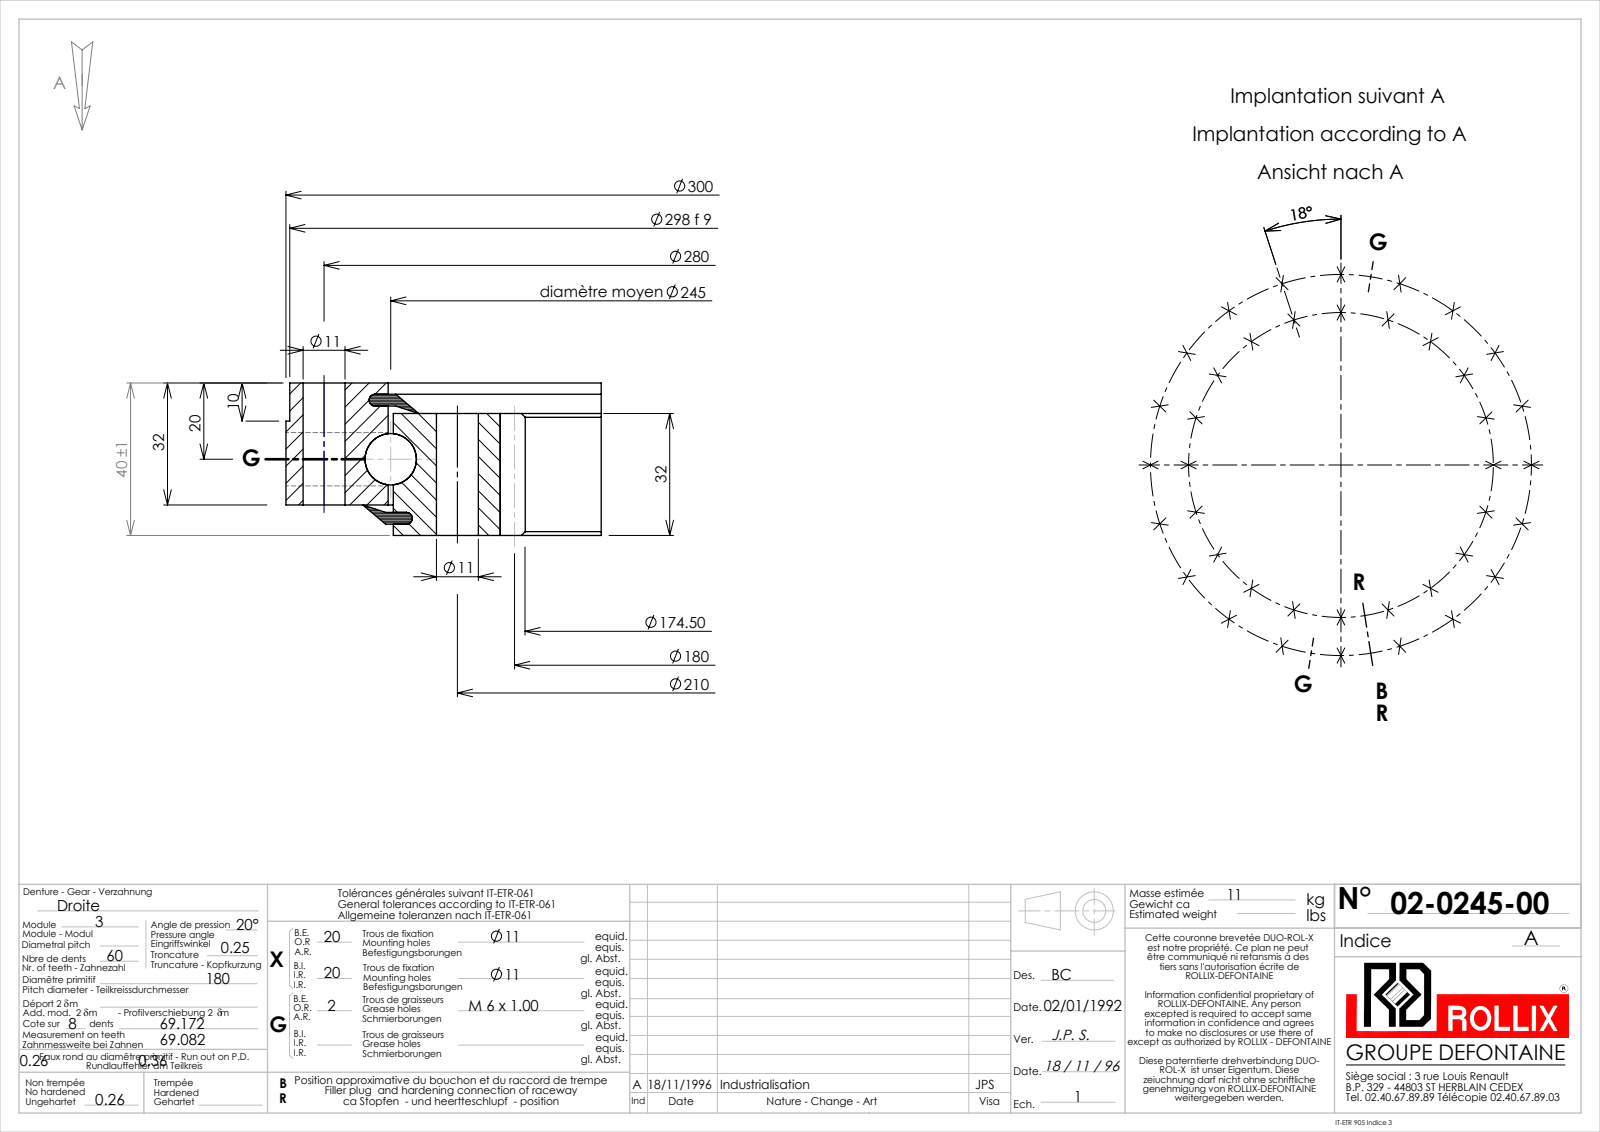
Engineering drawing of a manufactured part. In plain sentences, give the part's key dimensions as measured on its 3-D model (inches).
The part is named "02-0245-00". Its 3-D file was written by "SolidWorks 2016 (CONFIG_CONTROL_DESIGN)". It is 5 solids with 502 faces: 133 planar, 221 cylindrical and 148 other. Overall it measures 11.811 by 11.811 by 1.575 inches. Its volume is 73.59 cubic inches and its surface area 479.6 square inches. Round holes: 40 of diameter 0.433, 2 of diameter 0.197, 1 of diameter 9.699. Round bosses or shafts: 1 of diameter 11.811, 1 of diameter 11.732, 1 of diameter 9.593. Partial cylindrical surfaces (rounded edges, fillets, slot ends): 1 of radius 3.435, 1 of radius 3.691. The main face-to-face distances are 1.26, 0.315, 0.945, 1.575, 0.238, 1.337, 0.077, 1.022, 0.116, 1.459. The hole center spacings are 1.293, 6.689, 9.183, 2.032, 2.555, 3.754, 4.548, 5.778.
